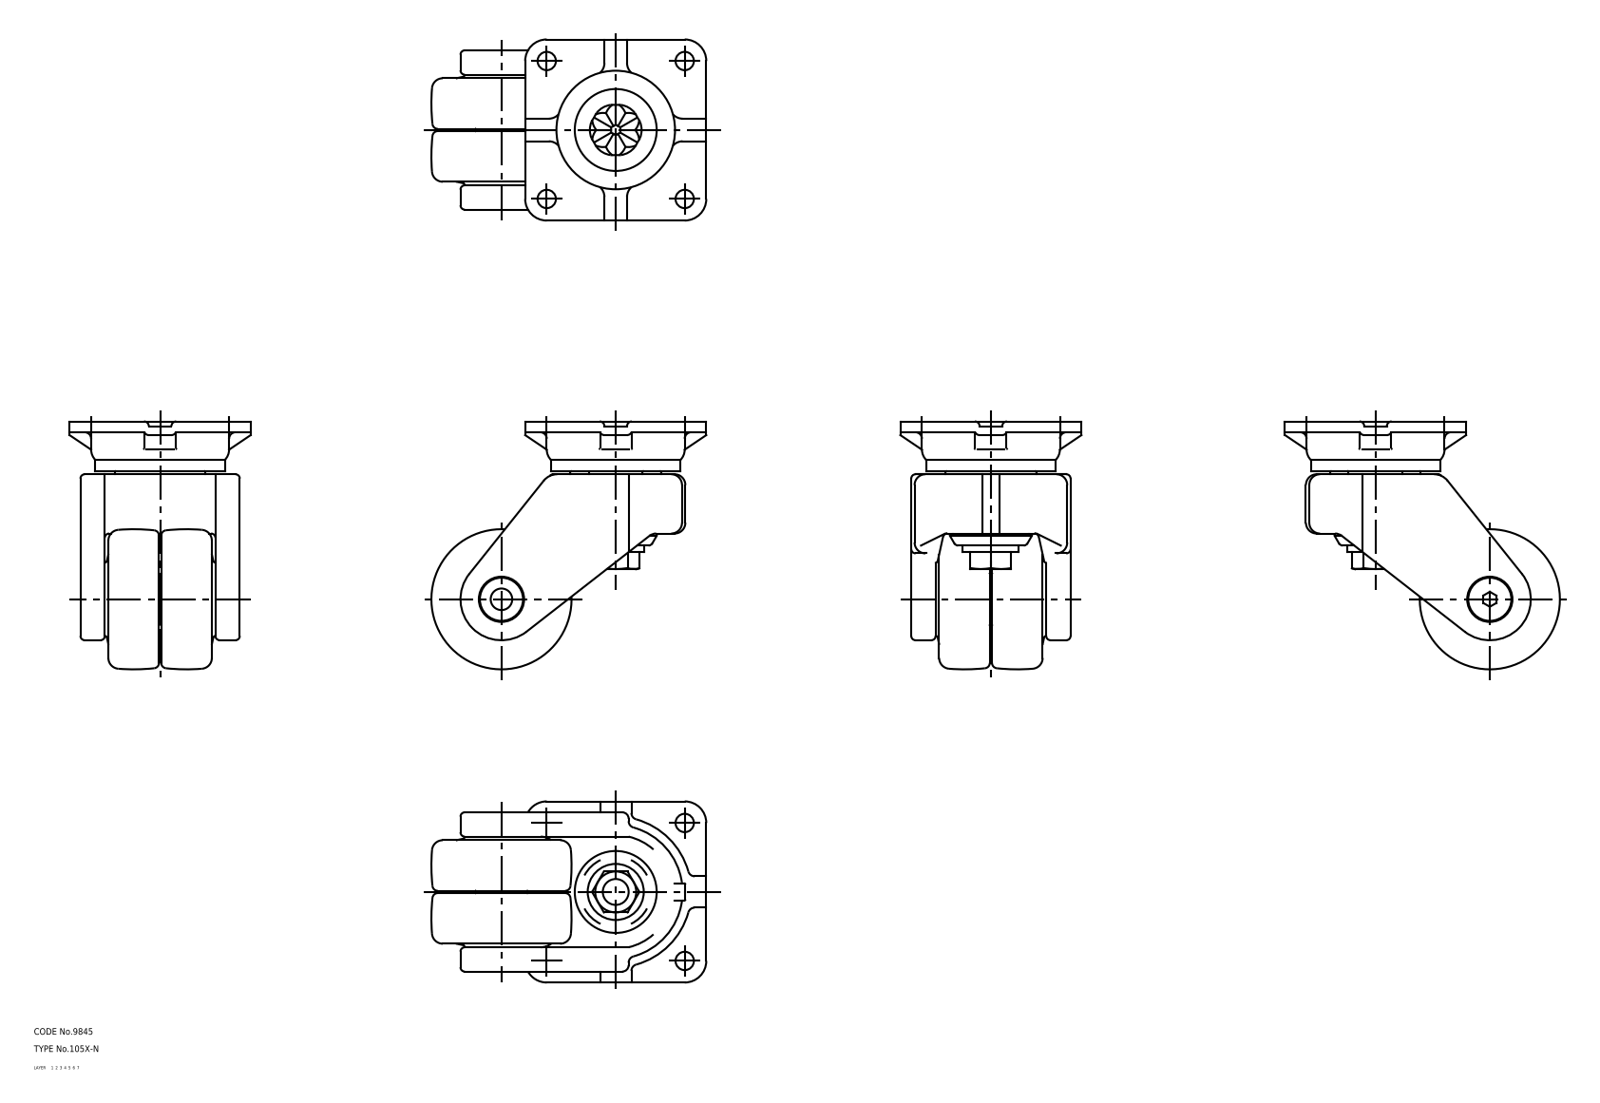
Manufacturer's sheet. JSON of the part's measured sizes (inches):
{"part_name": "wheel; mounting plate; main shaft; axle (+1 more)", "step_written_by": "CADfix (AUTOMOTIVE_DESIGN)", "units": "inches", "bodies": {"solids": 5, "faces": 444, "planar": 0, "cylindrical": 0, "other": 444}, "overall_size": [5.02, 4.528, 3.307], "volume_in3": 24.69, "surface_area_in2": 135.5}
